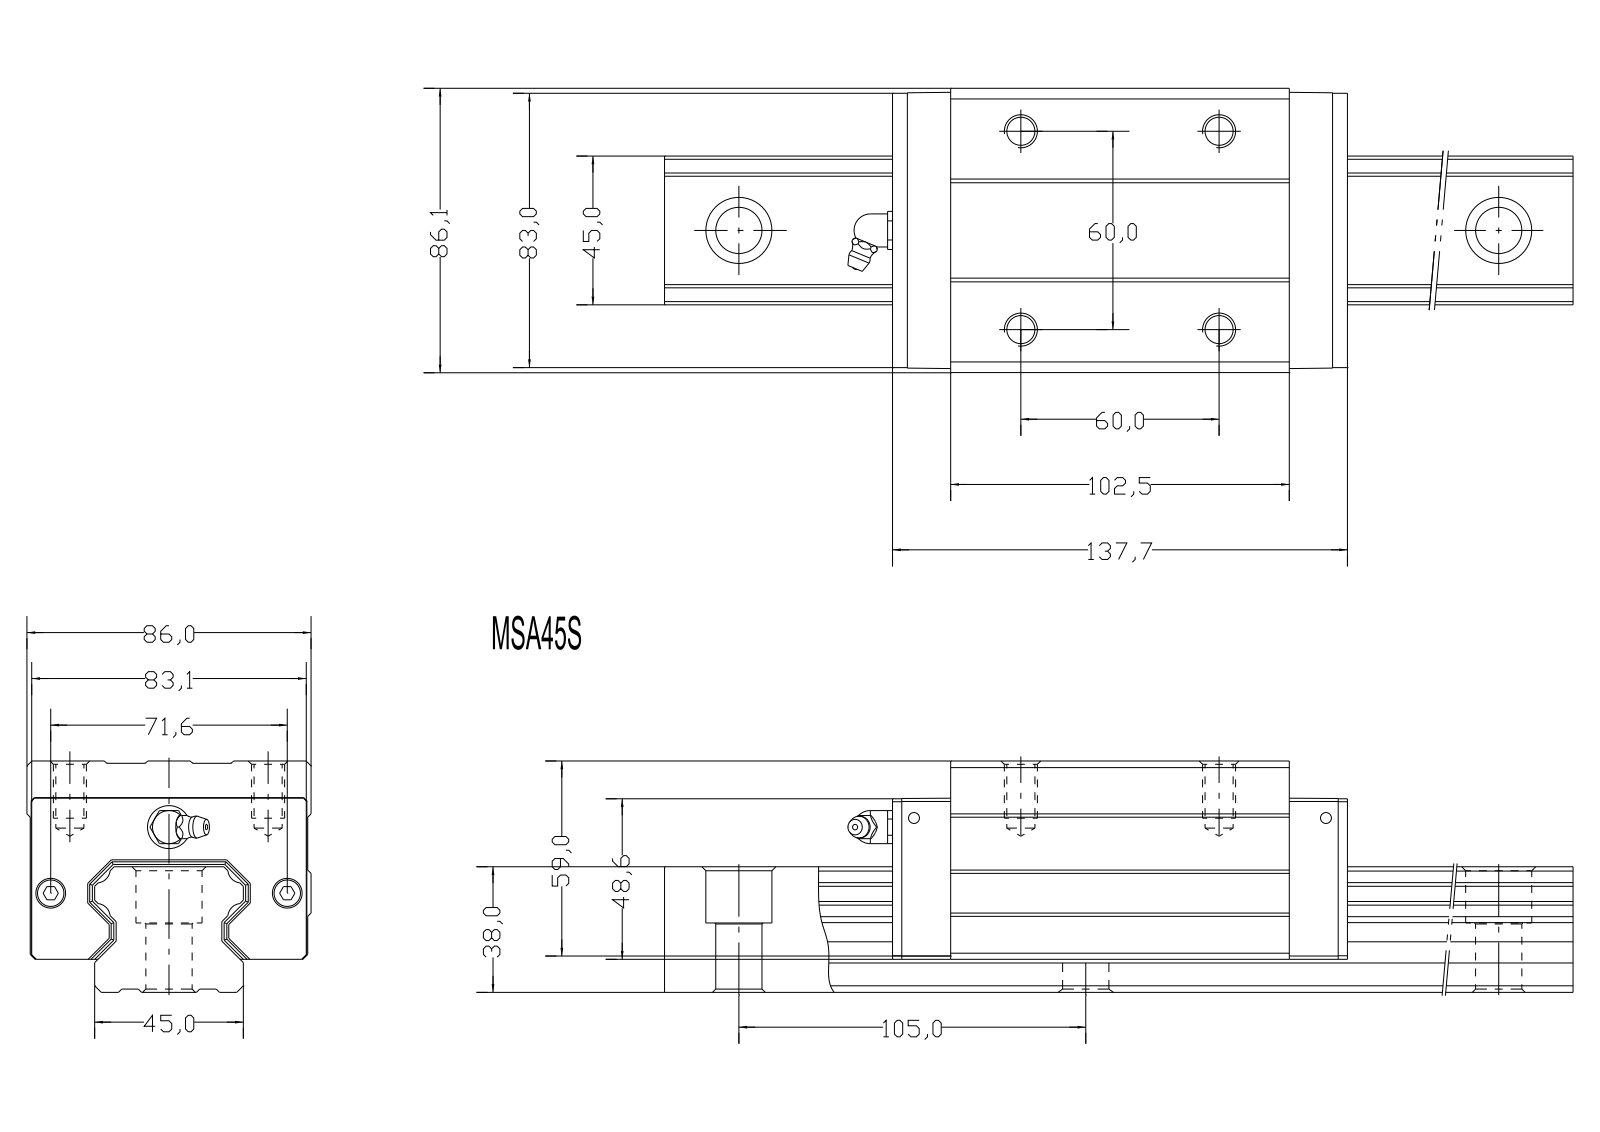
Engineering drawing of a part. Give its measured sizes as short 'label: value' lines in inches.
written by: Kubotek KeyCreator V6.5.2 (0407) (CONFIG_CONTROL_DESIGN)
unit: in
bodies: 3 solids, 201 faces (130 planar, 54 cylindrical, 17 other)
size: 14.173 × 3.386 × 2.756
volume: 61.57 in³; area: 202.5 in²
holes: 4× ⌀0.394, 4× ⌀0.551, 4× ⌀0.787, 2× ⌀0.177, 2× ⌀0.354, 1× ⌀0.512
bosses: 1× ⌀0.394
rounds: 4× R0.171
face distances: 1.496, 0.039, 1.26, 1.028, 2.28, 2.756, 0.394, 1.102, 2.362, 0.26
hole spacings: 1.476, 2.362, 3.456, 5.157, 7.476, 4.134, 1.615, 3.341
